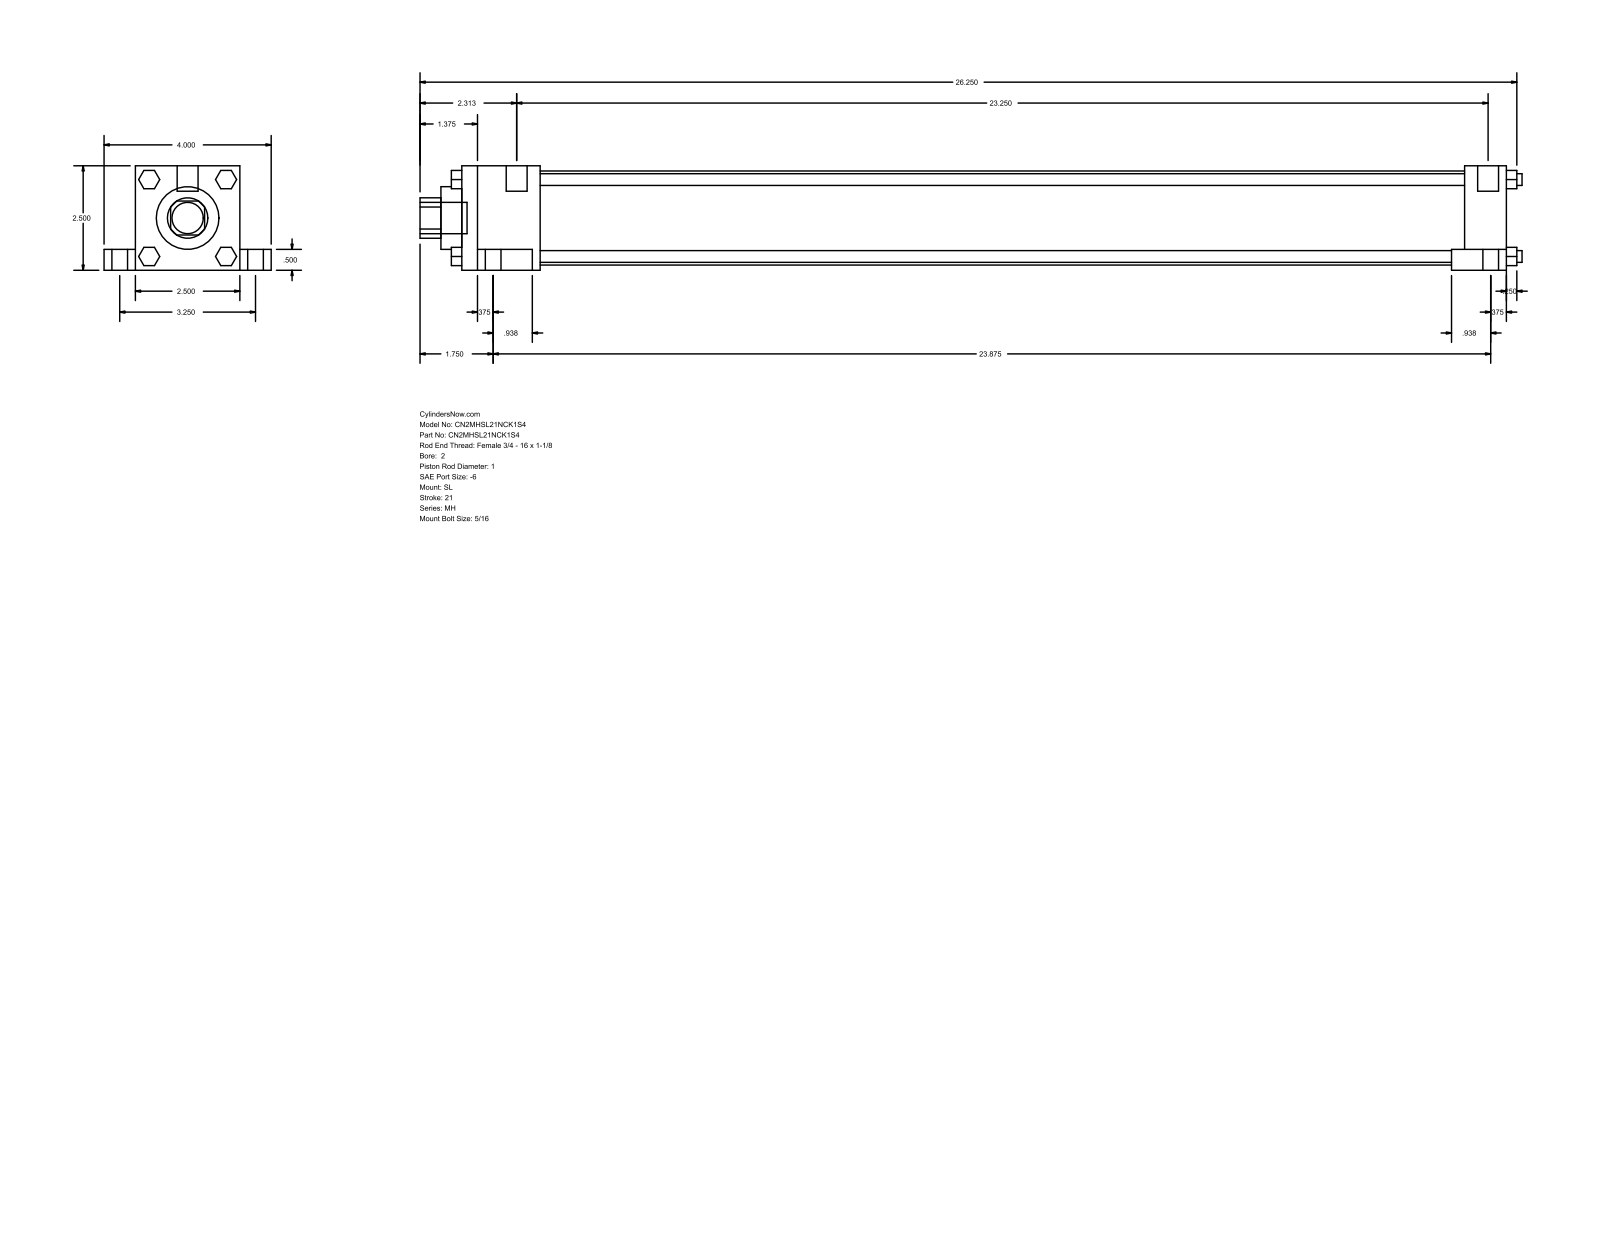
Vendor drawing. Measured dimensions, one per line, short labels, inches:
name: MH_SL__0200_1
written by: GSSL Pune (CONFIG_CONTROL_DESIGN)
unit: in
bodies: 0 solids, 148 faces (112 planar, 36 cylindrical, 0 other)
size: 26.375 × 4 × 2.5
holes: 1× ⌀1, 1× ⌀1.5, 1× ⌀2.25
bosses: 4× ⌀0.625, 4× ⌀0.375, 4× ⌀0.281, 4× ⌀0.219, 2× ⌀0.5, 1× ⌀0.75
rounds: 1× R0.484
face distances: 2.5, 25, 0.5, 0.75, 2, 3.25, 0.375, 1, 24, 1.875
